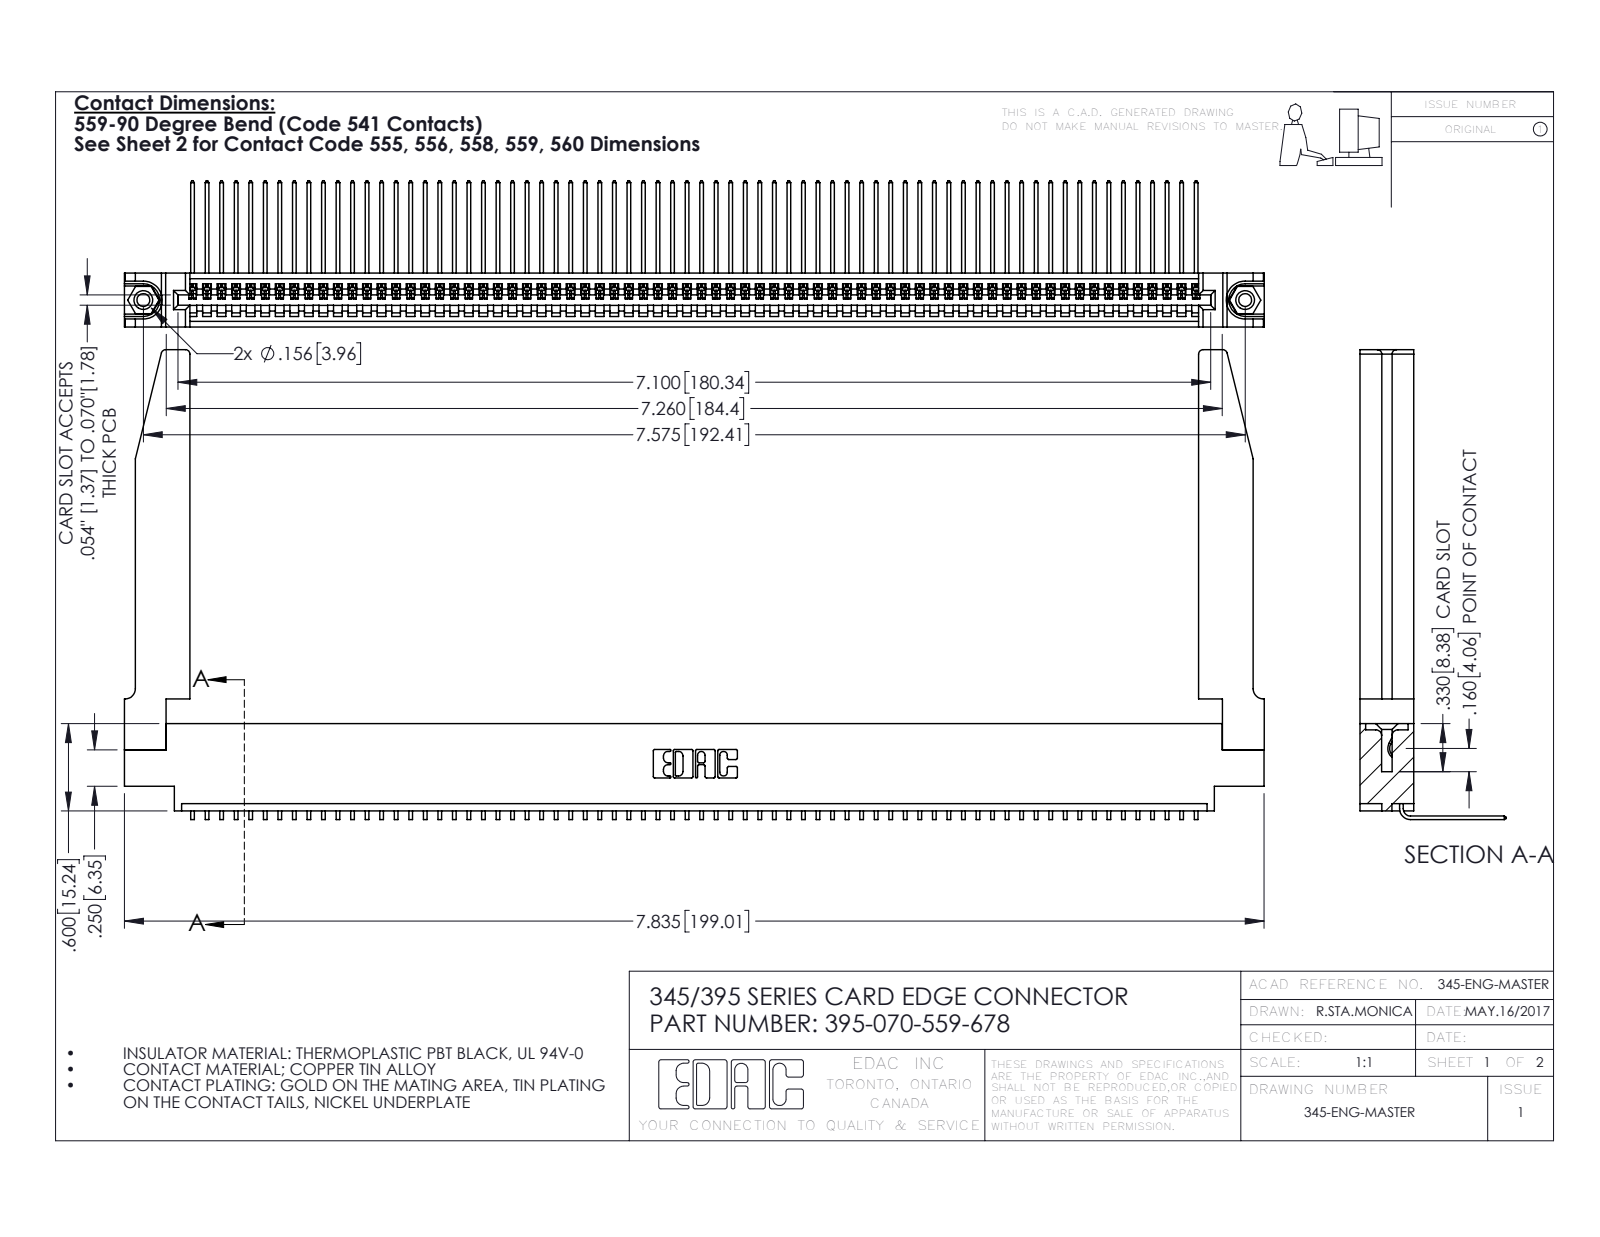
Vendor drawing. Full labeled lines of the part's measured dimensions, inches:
Part name (STEP PRODUCT): 395-070-559-678; 345-220-078_345-220-078; 345 Part_0.170 Offset - 0.156 Dia-TH; 345-250-001_345-250-001-102 (+1 more)
STEP written by: SolidWorks 2016 (CONFIG_CONTROL_DESIGN)
Units: inches
Bodies: 75 solids, 4564 faces (3166 planar, 1346 cylindrical, 52 other)
Overall size (bounding box): 7.836 × 3.229 × 1.005
Volume: 1.649 in³ · Surface area: 53.18 in²
Round holes (diameter × count): ⌀0.089 ×2, ⌀0.125 ×2, ⌀0.156 ×2, ⌀0.064 ×1
Round bosses / shafts (diameter × count): ⌀0.155 ×2
Partial cylindrical surfaces — rounded edges, fillets, slot ends (radius × count): R0.006 ×140, R0.01 ×22, R0.03 ×8, R0.007 ×6, R0.031 ×6, R0.026 ×3, R0.031 ×2, R0.04 ×2
Main face-to-face distances: 0.37, 0.072, 0.298, 0.098, 0.272, 0.025, 0.2, 0.225, 0.175, 0.149
Hole centre spacings: 0.27, 7.339, 7.575
